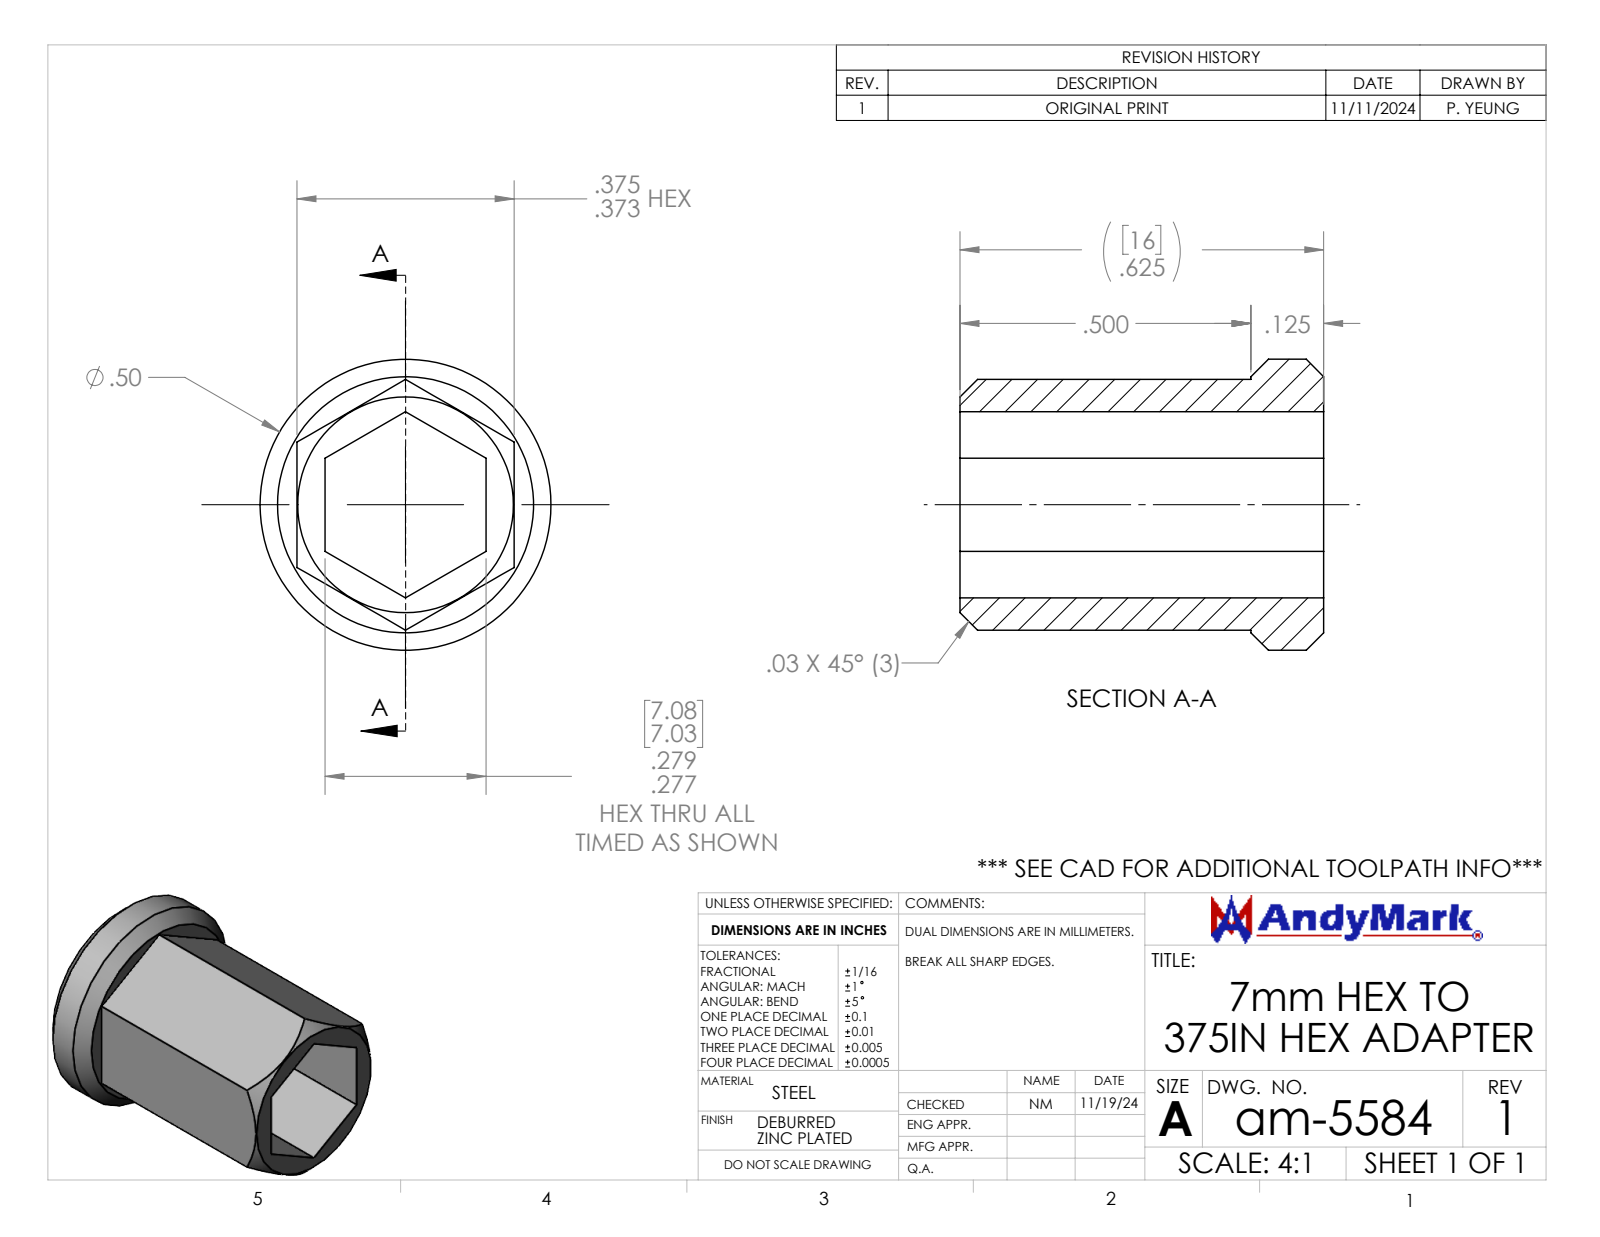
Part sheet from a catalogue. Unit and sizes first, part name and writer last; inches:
Units: inches
Overall size (bounding box): 0.625 × 0.5 × 0.5
Round bosses / shafts (diameter × count): ⌀0.5 ×1
Main face-to-face distances: 0.048, 0.325, 0.373, 0.048, 0.325, 0.276, 0.277, 0.625, 0.125, 0.5
Volume: 0.042 in³ · Surface area: 1.635 in²
Bodies: 1 solid, 23 faces (15 planar, 2 cylindrical, 6 other)
Part name (STEP PRODUCT): am-5584 7mm Hex to 0375IN Hex Adapter
STEP written by: SolidWorks 2024 (AUTOMOTIVE_DESIGN)
